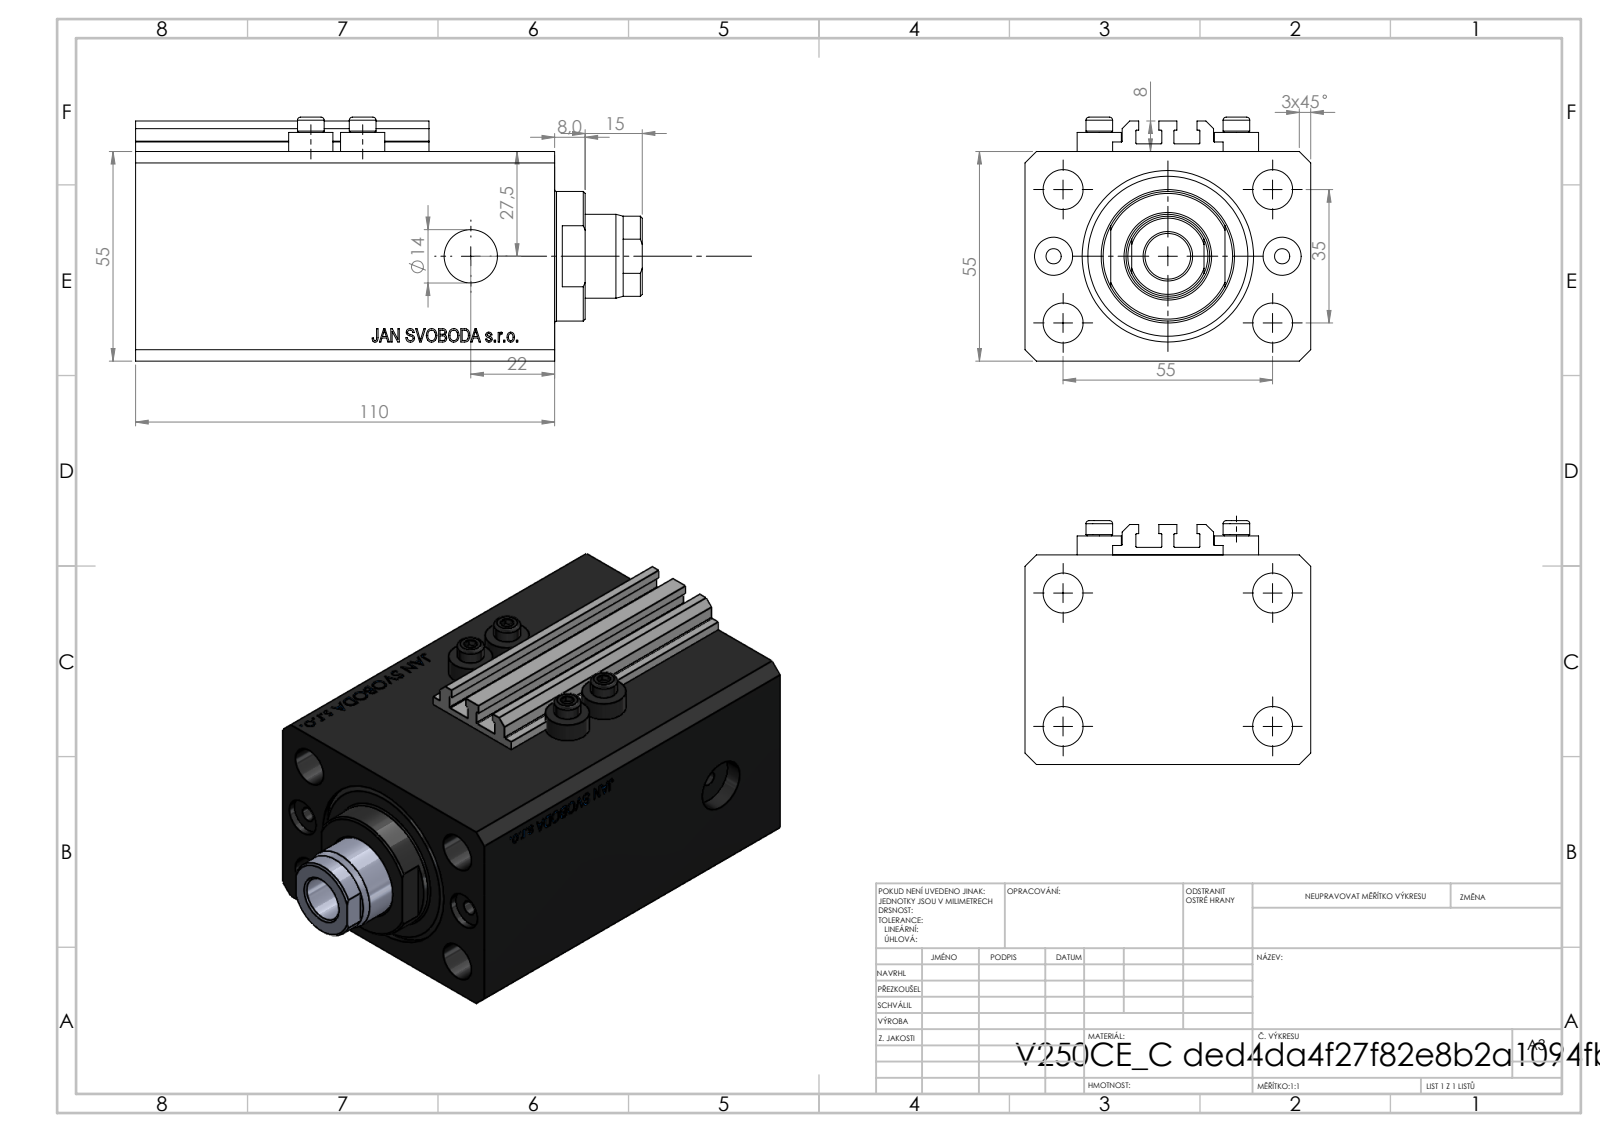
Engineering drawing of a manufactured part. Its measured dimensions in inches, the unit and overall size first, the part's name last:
Units: inches
Overall size (bounding box): 5.236 × 2.953 × 2.52
Round holes (diameter × count): ⌀0.157 ×7, ⌀0.413 ×4, ⌀0.394 ×2, ⌀0.551 ×2, ⌀0.472 ×1, ⌀0.866 ×1, ⌀1.26 ×1, ⌀1.772 ×1
Round bosses / shafts (diameter × count): ⌀0.457 ×4, ⌀0.276 ×4, ⌀1.339 ×1
Partial cylindrical surfaces — rounded edges, fillets, slot ends (radius × count): R0.008 ×10, R0.413 ×1
Main face-to-face distances: 2.165, 2.953, 0.394, 4.331, 3.858, 0.472, 3.465, 3.937, 0.098, 0.118
Hole centre spacings: 0.696, 1.283, 2.366, 0.535, 1.181, 1.378, 1.417, 1.515
Volume: 25.22 in³ · Surface area: 140.2 in²
Bodies: 8 solids, 1023 faces (501 planar, 82 cylindrical, 440 other)
Part name (STEP PRODUCT): V250CE_C_vnitrni cast pro vysunuti; V250CE_C_VCP; ALLEN BOLT V250CE; V250CE_C
STEP written by: SolidWorks 2019 (CONFIG_CONTROL_DESIGN)
